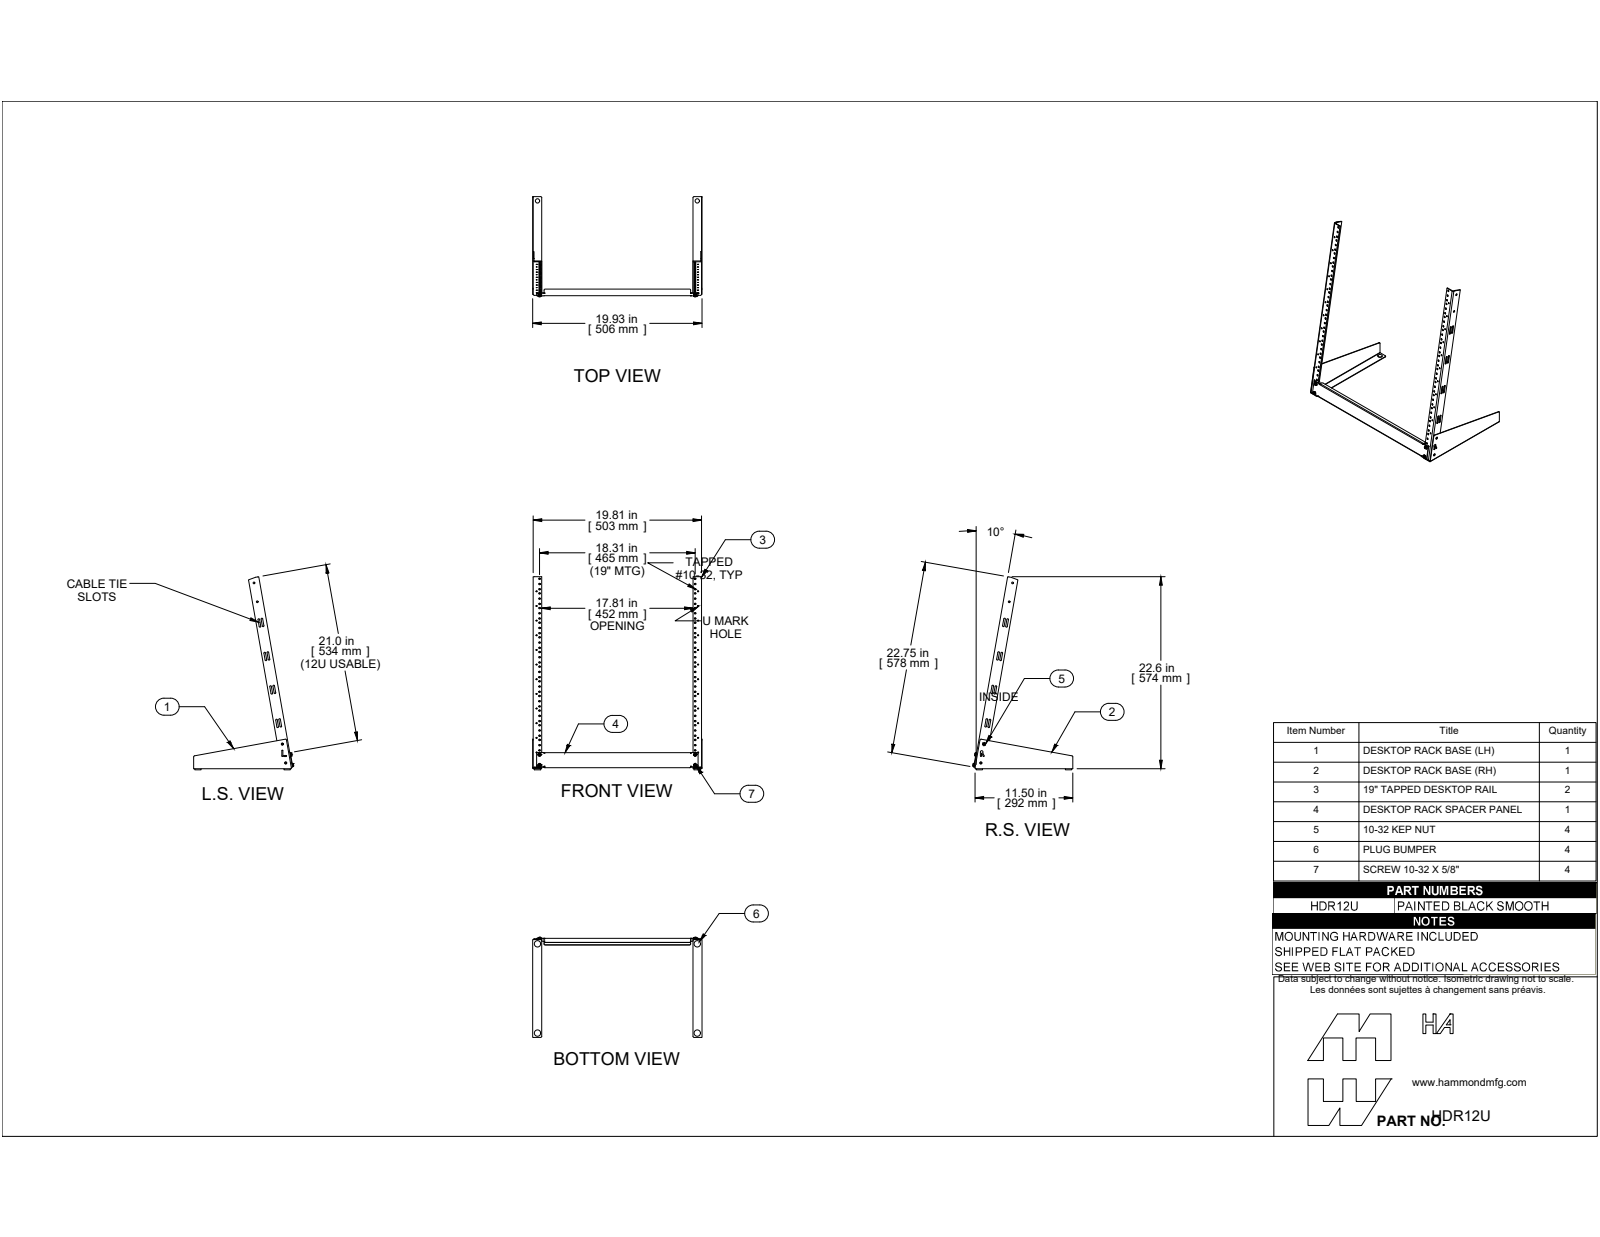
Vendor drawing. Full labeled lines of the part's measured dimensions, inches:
Part name (STEP PRODUCT): HDR12UBK
STEP written by: SolidWorks 2019 (CONFIG_CONTROL_DESIGN)
Units: inches
Bodies: 21 solids, 464 faces (232 planar, 224 cylindrical, 8 other)
Overall size (bounding box): 22.714 × 19.926 × 11.773
Volume: 16.26 in³ · Surface area: 467.9 in²
Round holes (diameter × count): ⌀0.177 ×78, ⌀0.125 ×24, ⌀0.198 ×4, ⌀0.206 ×4, ⌀0.5 ×4, ⌀0.156 ×2, ⌀0.189 ×2
Round bosses / shafts (diameter × count): ⌀0.368 ×8, ⌀0.75 ×4, ⌀0.189 ×4, ⌀0.256 ×2, ⌀0.19 ×2
Partial cylindrical surfaces — rounded edges, fillets, slot ends (radius × count): R0.094 ×16, R0.125 ×14, R0.029 ×4, R0.063 ×4, R0.086 ×4, R0.062 ×3, R0.048 ×2, R0.143 ×2
Main face-to-face distances: 0.057, 0.095, 19.87, 19.813, 0.152, 19.927, 0.152, 19.774, 19.717, 0.095
Hole centre spacings: 3.5, 1.125, 7, 1.75, 5.25, 10.5, 0.625, 5.875
